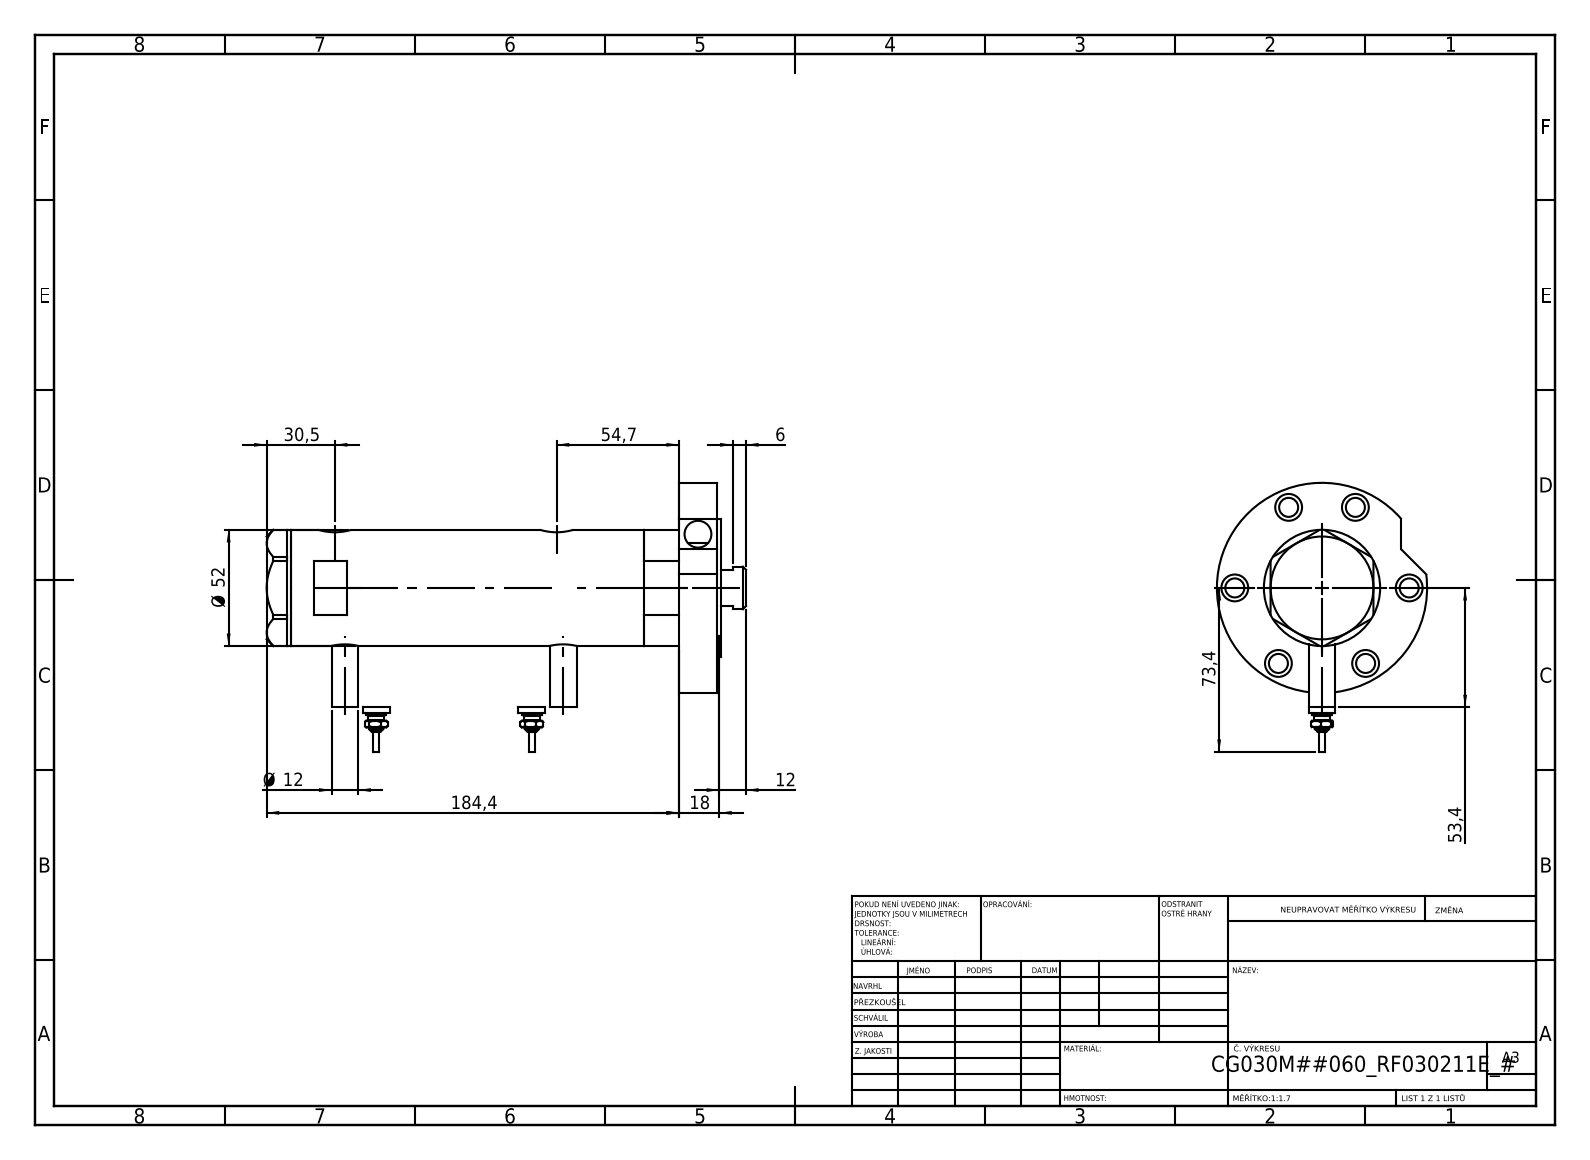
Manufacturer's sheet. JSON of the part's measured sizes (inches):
{"part_name": "Switch; V270CG_VC; V270CG_RF211E; V270CG_MIDDLE (+2 more)", "step_written_by": "SolidWorks 2019 (CONFIG_CONTROL_DESIGN)", "units": "inches", "bodies": {"solids": 7, "faces": 270, "planar": 104, "cylindrical": 102, "other": 64}, "overall_size": [8.441, 4.74, 3.701], "volume_in3": 28.97, "surface_area_in2": 175.6, "round_holes": [[0.472, 7], [0.335, 6], [0.383, 2], [0.492, 2], [0.591, 2], [0.256, 1], [0.787, 1], [0.846, 1], [1.181, 1], [1.299, 1], [1.575, 1], [1.732, 1]], "round_bosses_or_shafts": [[0.472, 4], [0.354, 2], [0.276, 2], [0.177, 2], [0.098, 2], [3.701, 1], [2.441, 1], [2.047, 1]], "face_to_face_distances": [0.669, 6.827, 7.496, 0.079, 7.575, 4.783, 2.043, 2.713, 0.433, 8.008], "hole_center_spacings": [1.535, 1.706, 2.553, 2.659, 2.754, 3.064, 0.114, 0.177]}
